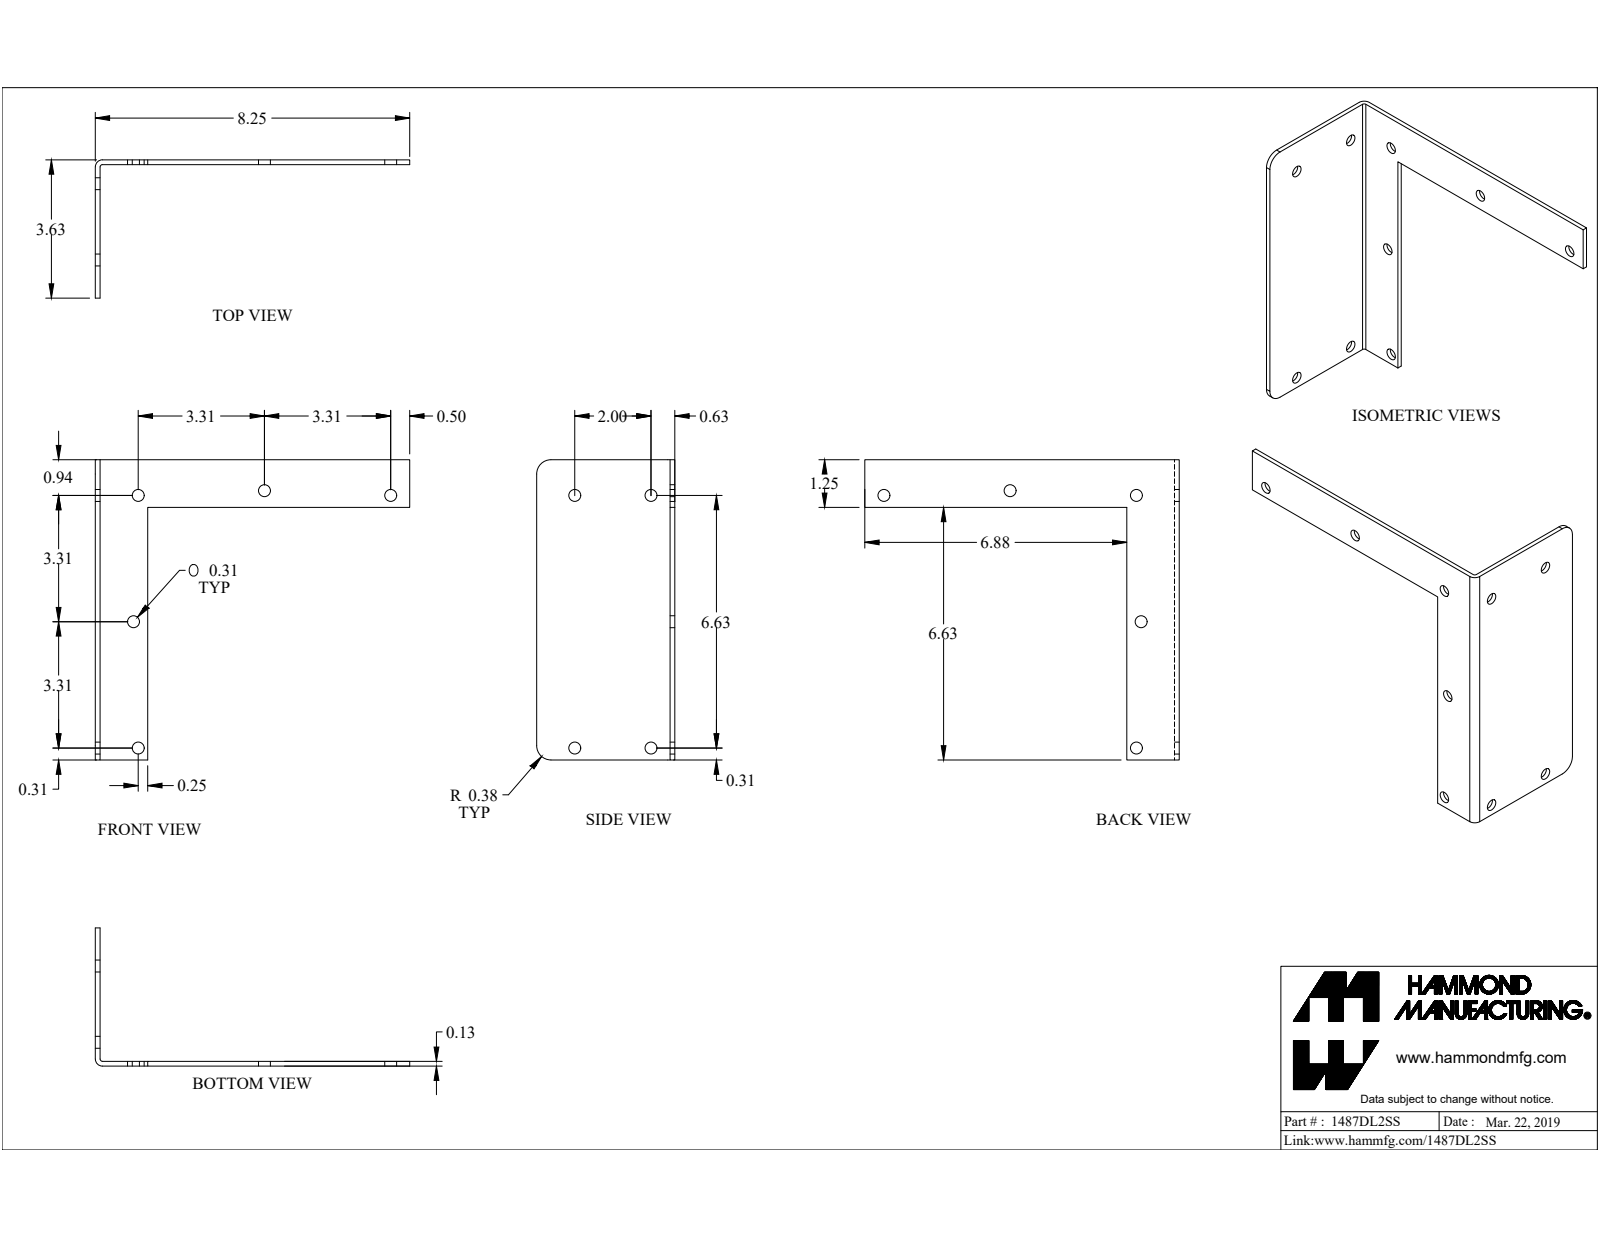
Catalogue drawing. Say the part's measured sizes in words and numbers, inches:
The part is named "1487DL2SS". Its 3-D file was written by "SolidWorks 2019 (CONFIG_CONTROL_DESIGN)". It is 6 solids with 228 faces: 144 planar, 49 cylindrical and 35 other. Overall it measures 10.25 by 8.125 by 4.875 inches. Its volume is 6.228 cubic inches and its surface area 122.2 square inches. Round holes: 9 of diameter 0.313, 1 of diameter 0.196, 1 of diameter 0.258, 1 of diameter 0.35. Round bosses or shafts: 1 of diameter 0.5, 1 of diameter 0.25. Partial cylindrical surfaces (rounded edges, fillets, slot ends): 6 of radius 0.02, 6 of radius 0.375, 1 of radius 0.06, 1 of radius 0.185, 1 of radius 0.25. The main face-to-face distances are 0.125, 0.03, 1.25, 7.845, 7.875, 1.375, 3.5, 3.625, 6.595, 6.625. The hole center spacings are 6.625, 2, 3.316, 6.92, 0.699, 1.167, 2.643, 3.314.
